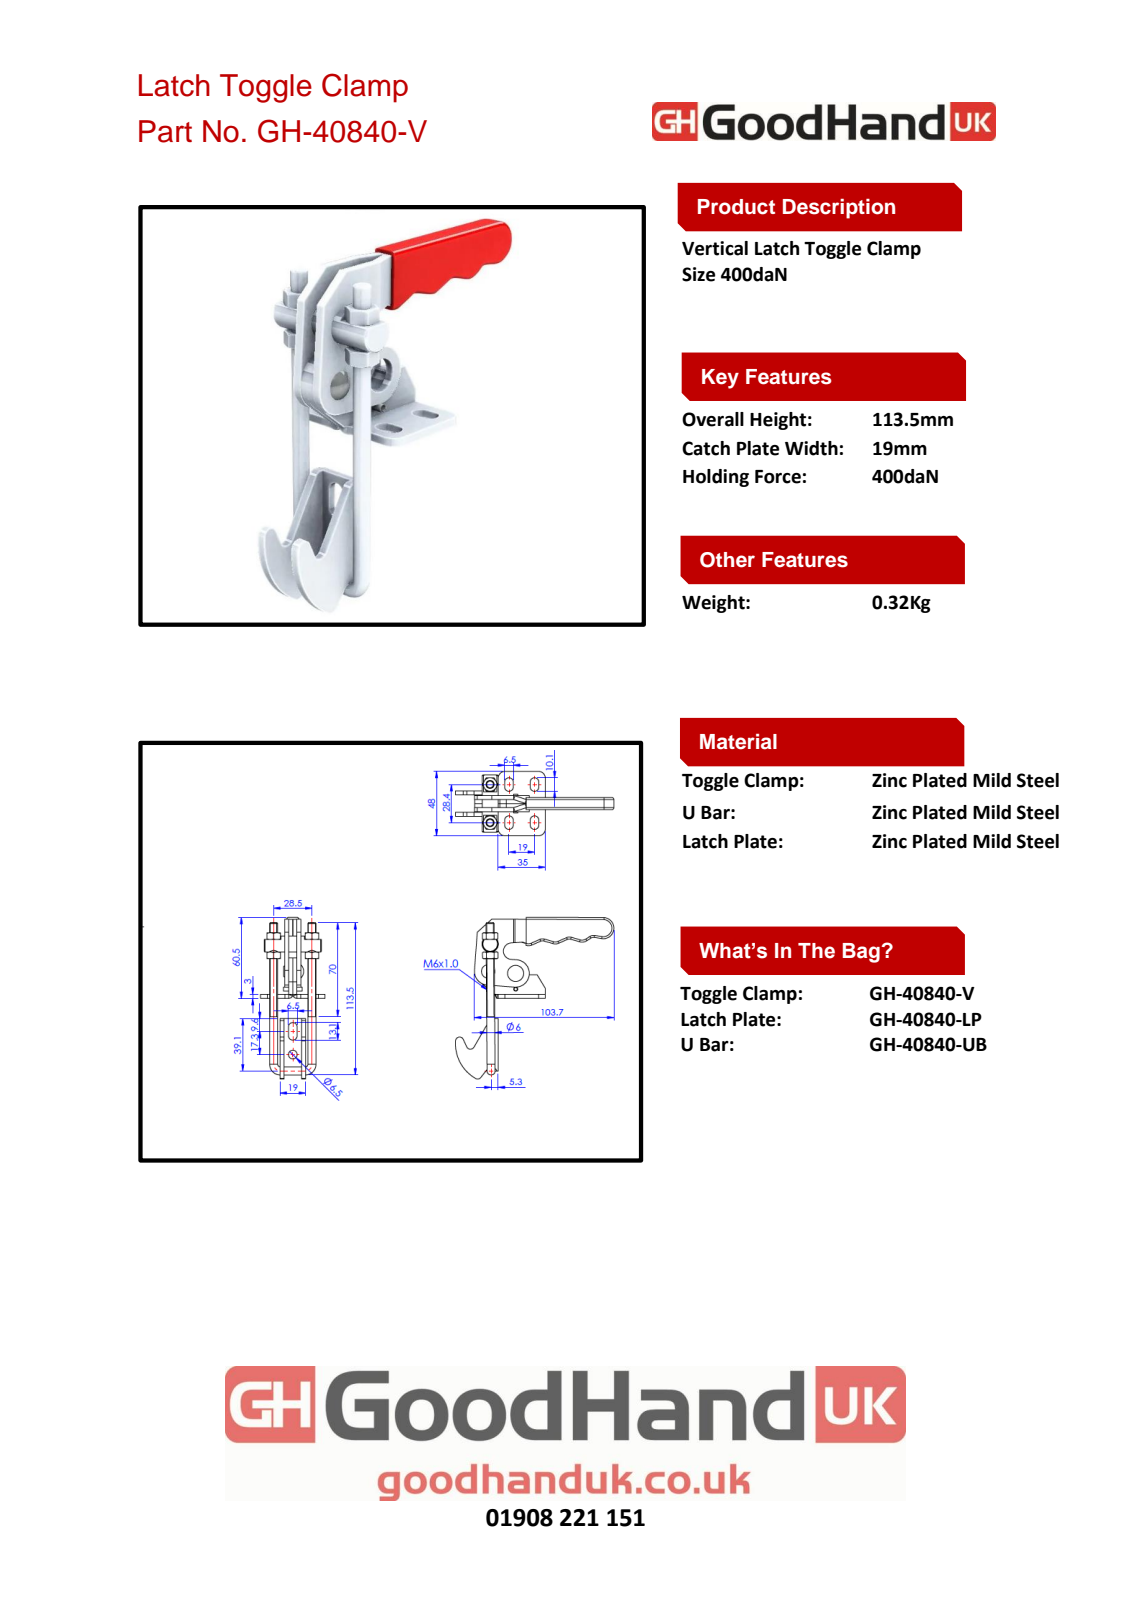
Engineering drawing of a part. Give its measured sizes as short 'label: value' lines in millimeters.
name: Group3^GH-40840-V(簡化); Group6^GH-40840-V(簡化); GH-40840 LP-1^GH-40840-V(簡化); Group1^GH-40840-V(簡化) (+2 more)
written by: SolidWorks 2016 (AUTOMOTIVE_DESIGN)
unit: mm
bodies: 7 solids, 637 faces (287 planar, 143 cylindrical, 207 other)
size: 120.53 × 117.94 × 47.98
volume: 45 408 mm³; area: 29 701 mm²
holes: 3× ⌀6, 3× ⌀6.5, 2× ⌀11.9, 1× ⌀1.34, 1× ⌀2.4, 1× ⌀5
bosses: 1× ⌀3, 1× ⌀1.28
rounds: 10× R3.25, 8× R3.01, 6× R5, 4× R3, 3× R0.51, 3× R0.54, 3× R3.5, 3× R6.5
face distances: 3, 1.5, 9, 12.5, 3.5, 7.5, 10.5, 6, 5, 2
hole spacings: 20.5, 7.01, 8.7, 11.7, 24.38, 27.03, 28.5, 29
